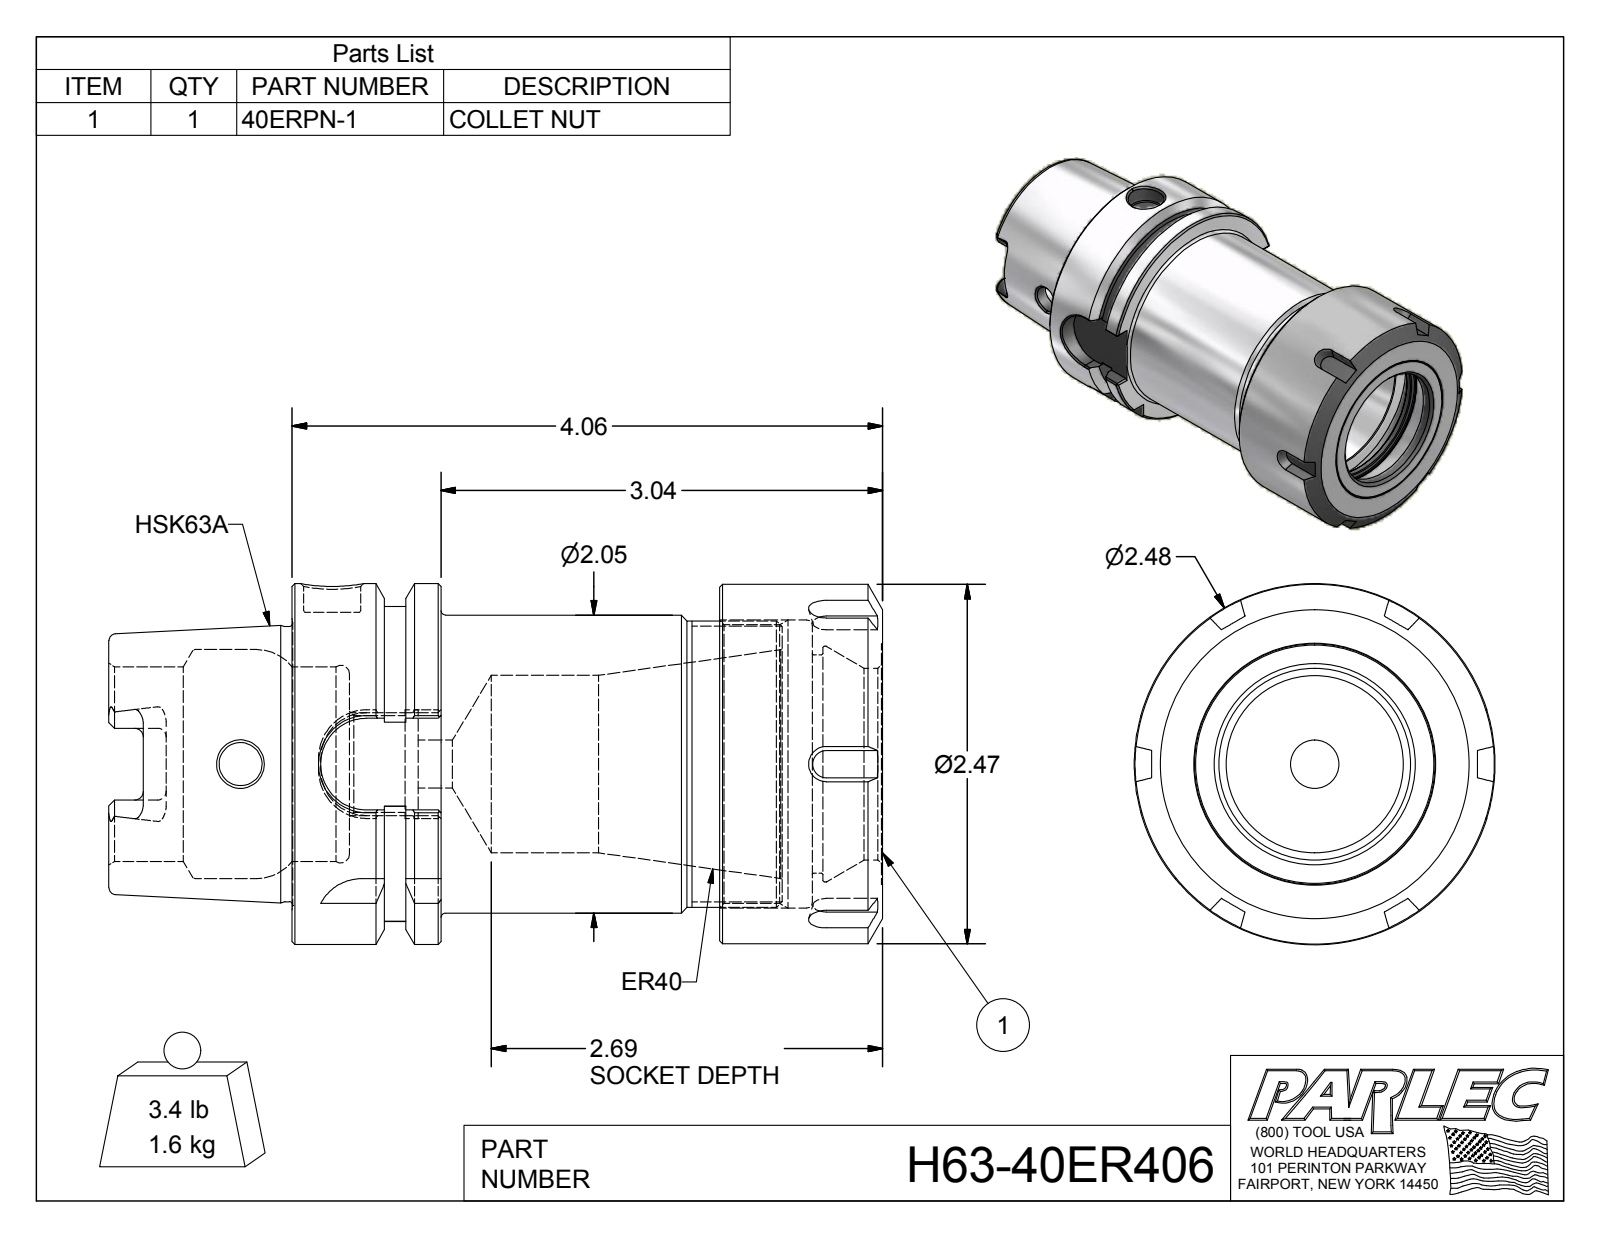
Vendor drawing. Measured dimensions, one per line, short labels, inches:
name: H63-40ER406; H63-40ER4-1; 40ERPN
written by: Autodesk Inventor 2012 (AUTOMOTIVE_DESIGN)
unit: in
bodies: 2 solids, 190 faces (79 planar, 42 cylindrical, 69 other)
size: 5.32 × 2.48 × 2.48
volume: 12.12 in³; area: 78.63 in²
holes: 1× ⌀0.295, 1× ⌀0.331, 1× ⌀0.394, 1× ⌀0.666, 1× ⌀0.749, 1× ⌀1.22, 1× ⌀1.318, 1× ⌀1.339, 1× ⌀1.5, 1× ⌀1.575, 1× ⌀1.62, 1× ⌀1.916
bosses: 1× ⌀2.48, 1× ⌀2.47, 1× ⌀2.047, 1× ⌀1.969, 1× ⌀1.891
rounds: 6× R0.059, 4× R0.113, 4× R0.315, 1× R1.083
face distances: 1.12, 2.94, 4.06, 1.024, 3.576, 0.636, 0.484, 0.241, 0.389, 1.917
